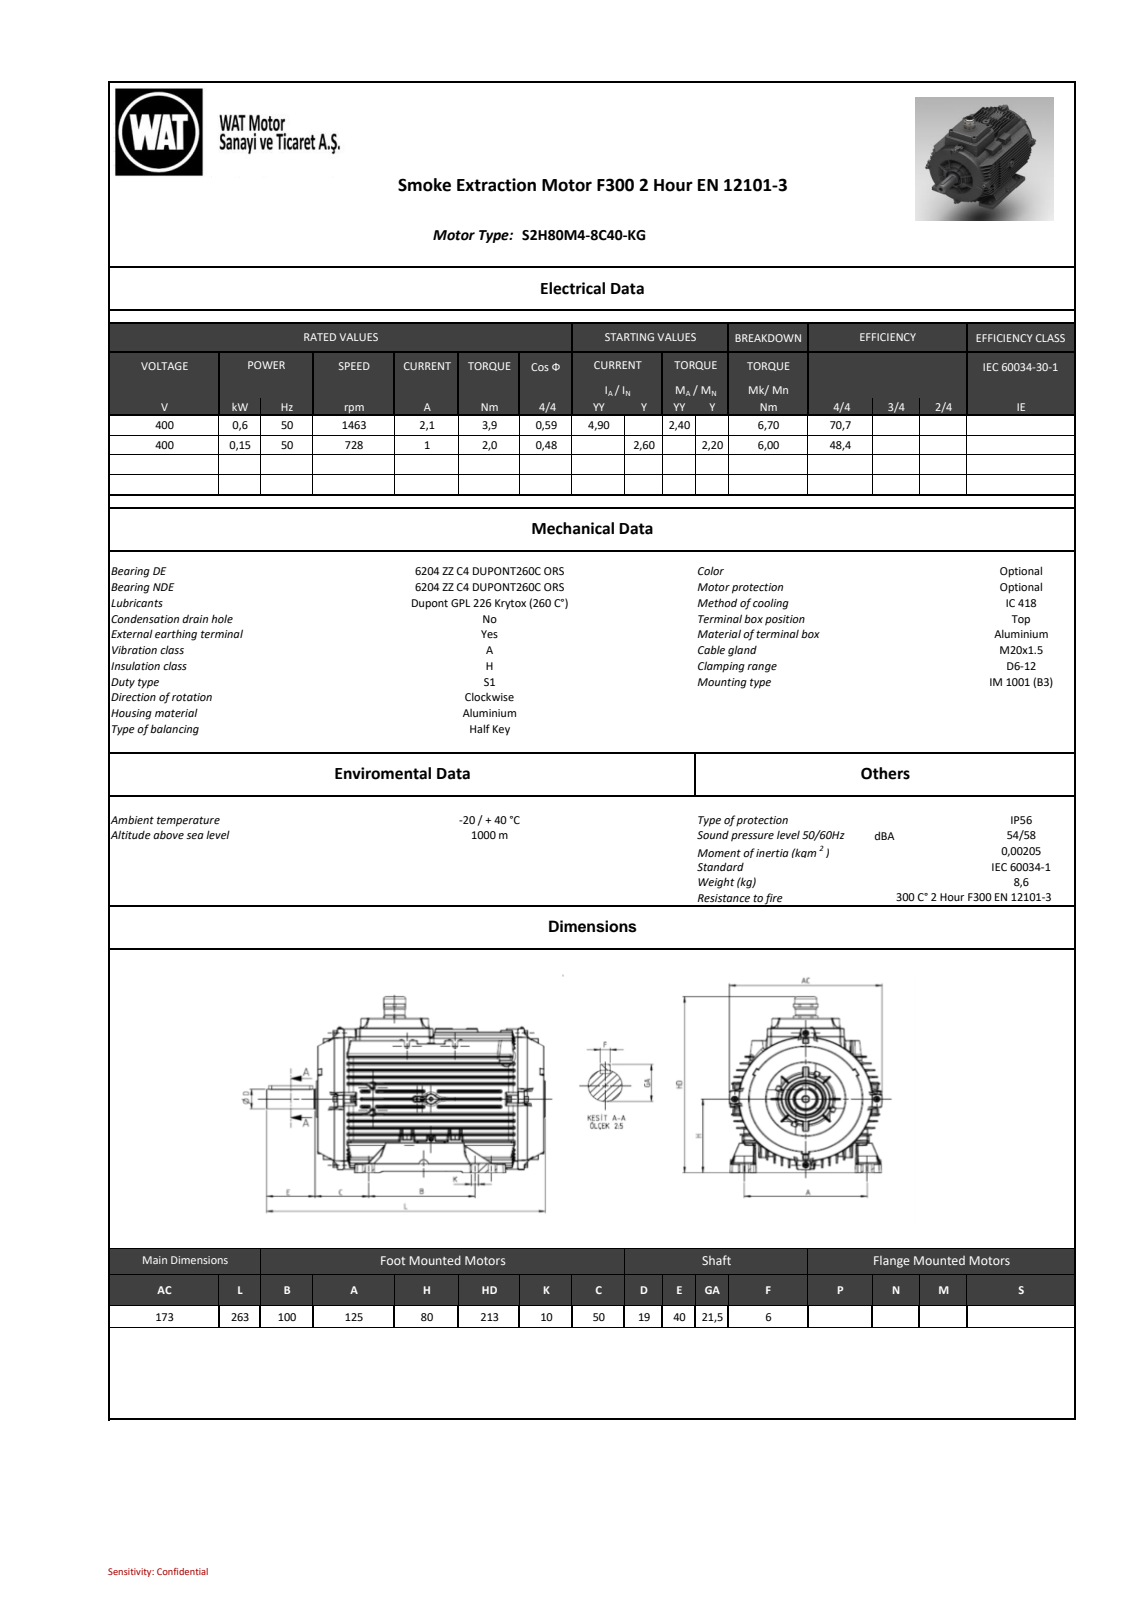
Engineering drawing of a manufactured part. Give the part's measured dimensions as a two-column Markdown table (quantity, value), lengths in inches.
| quantity | value |
| --- | --- |
| part name | 2603BE5CCA1Ccy93 |
| STEP written by | SIEMENS PLM Software NX 11.0 (AUTOMOTIVE_DESIGN) |
| units | inches |
| bodies | 0 solids, 6405 faces (1138 planar, 1739 cylindrical, 3528 other) |
| overall size | 10.354 × 8.386 × 6.063 |
| round holes (diameter × count) | 0.146 × 4, 0.118 × 3, 0.157 × 1, 0.252 × 1, 0.551 × 1, 0.945 × 1, 1.094 × 1, 1.102 × 1, 1.181 × 1 |
| round bosses / shafts (diameter × count) | 0.335 × 8, 0.197 × 8, 0.362 × 4, 0.315 × 4, 5.768 × 1, 1.161 × 1, 0.933 × 1, 0.882 × 1 |
| partial cylindrical surfaces (radius × count) | 0.02 × 443, 0.039 × 361, 0.031 × 328, 0.008 × 65, 0.079 × 29, 0.197 × 17, 0.157 × 8, 0.315 × 8 |
| main face-to-face distances | 1.652, 0.408, 0.826, 2.06, 2.342, 0.413, 0.413, 0.82, 1.239, 0.282 |
| hole center spacings | 1.004, 0.787, 1.739, 1, 1.005, 1.007, 1.739 |
